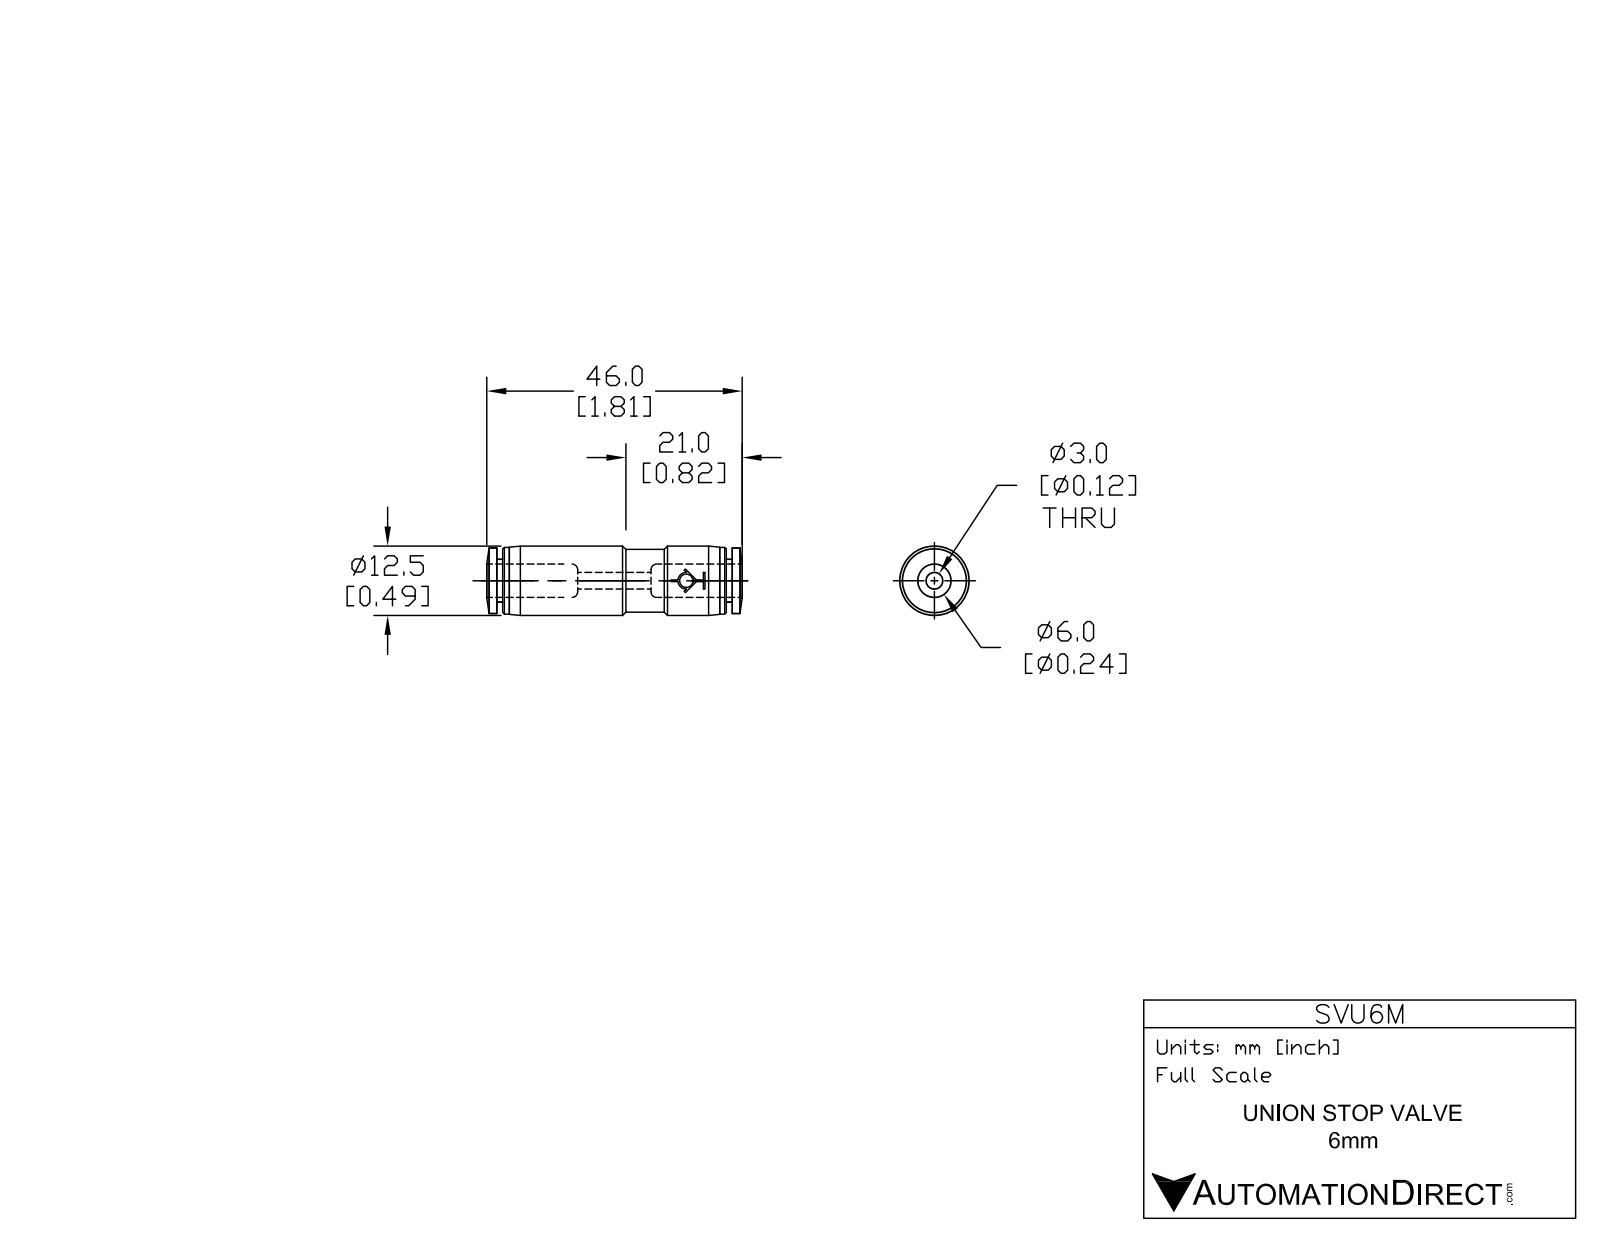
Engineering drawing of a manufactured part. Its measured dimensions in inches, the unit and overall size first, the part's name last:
Units: inches
Overall size (bounding box): 1.811 × 0.496 × 0.492
Round holes (diameter × count): ⌀0.094 ×1, ⌀0.177 ×1, ⌀0.248 ×1
Round bosses / shafts (diameter × count): ⌀0.492 ×1, ⌀0.472 ×1, ⌀0.465 ×1, ⌀0.445 ×1, ⌀0.303 ×1
Partial cylindrical surfaces — rounded edges, fillets, slot ends (radius × count): R0.059 ×1, R0.25 ×1
Main face-to-face distances: 0.041, 1.628, 1.669, 1.587, 0.575, 1.094, 0.533, 1.053, 0.52, 0.071
Volume: 0.242 in³ · Surface area: 4.64 in²
Bodies: 1 solid, 76 faces (26 planar, 30 cylindrical, 20 other)
Part name (STEP PRODUCT): SVU6M
STEP written by: SolidWorks 2015 (AUTOMOTIVE_DESIGN)
